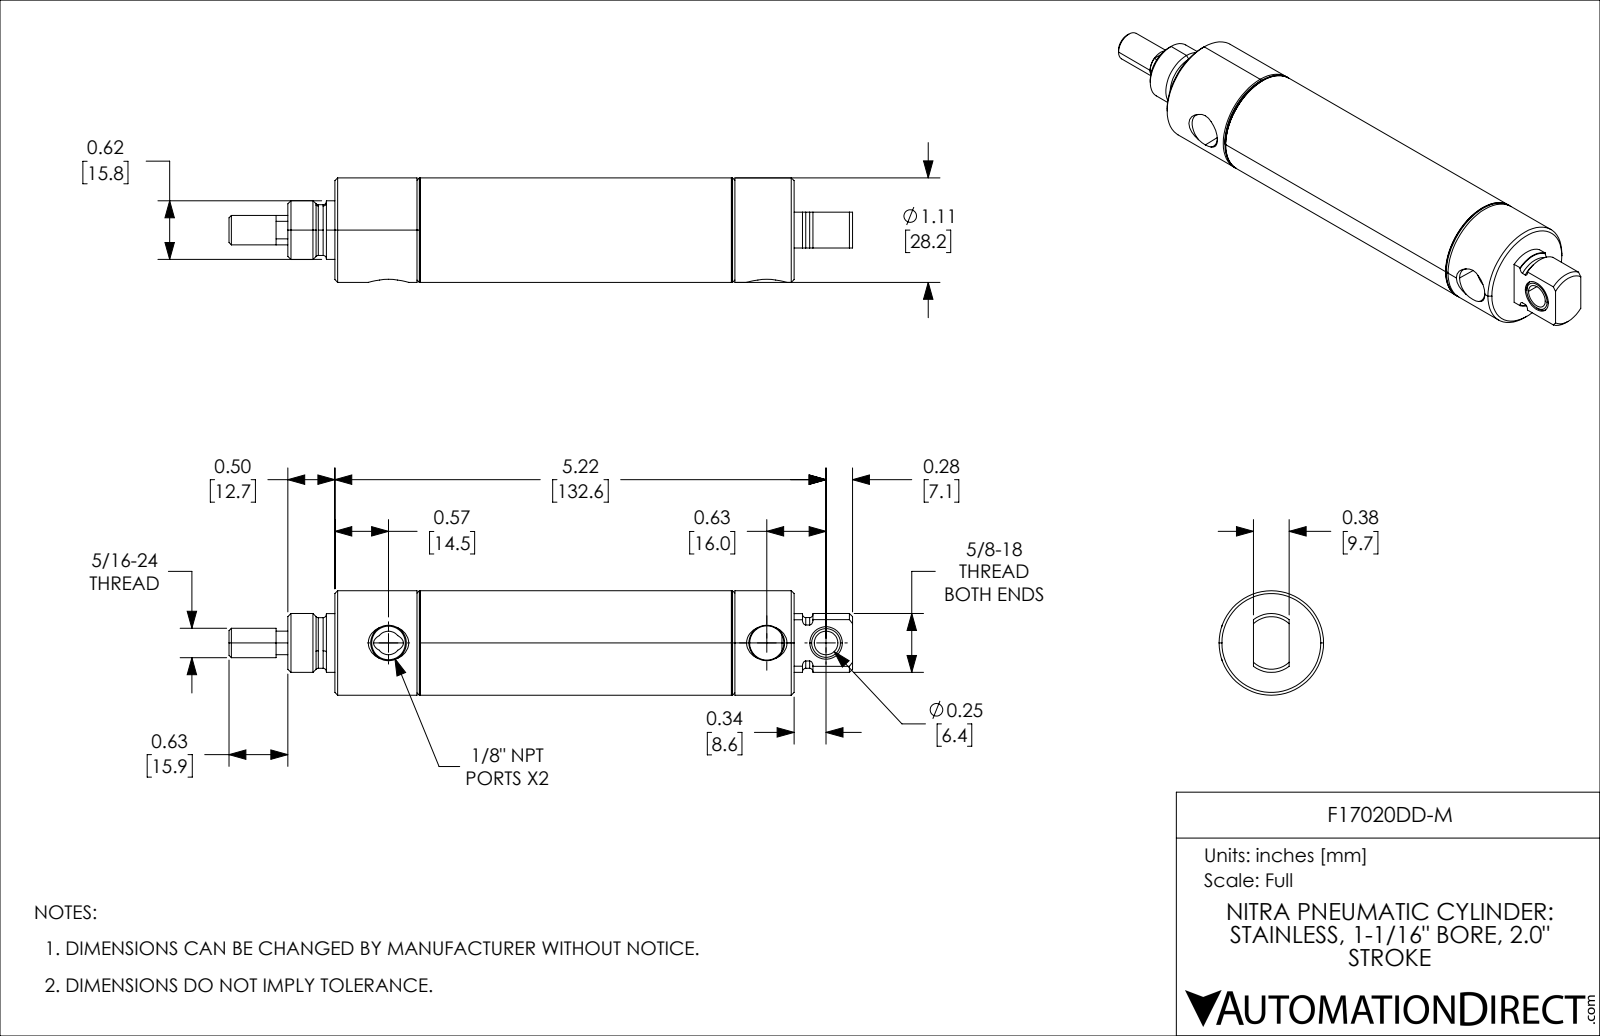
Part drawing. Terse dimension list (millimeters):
name: F17020DD-M_5; F17020DD-M_9; F17020DD-M_11; F17020DD-M (+2 more)
written by: SolidWorks 2021 (CONFIG_CONTROL_DESIGN)
unit: mm
bodies: 5 solids, 156 faces (30 planar, 58 cylindrical, 68 other)
size: 168.28 × 28.19 × 28.19
volume: 50 493 mm³; area: 32 250 mm²
holes: 1× ⌀6.38, 1× ⌀8.53, 1× ⌀8.78, 1× ⌀9.25, 1× ⌀9.53, 1× ⌀19.05, 1× ⌀25.7
bosses: 1× ⌀28.19, 1× ⌀27.23, 1× ⌀15.88, 1× ⌀15.81, 1× ⌀13.68, 1× ⌀7.94, 1× ⌀7.92
rounds: 1× R3.17, 1× R6.84
face distances: 22.22, 50.8, 73.02, 95.35, 44.55, 22.33, 28.58, 79.38, 101.6, 123.93
hole spacings: 16.01
